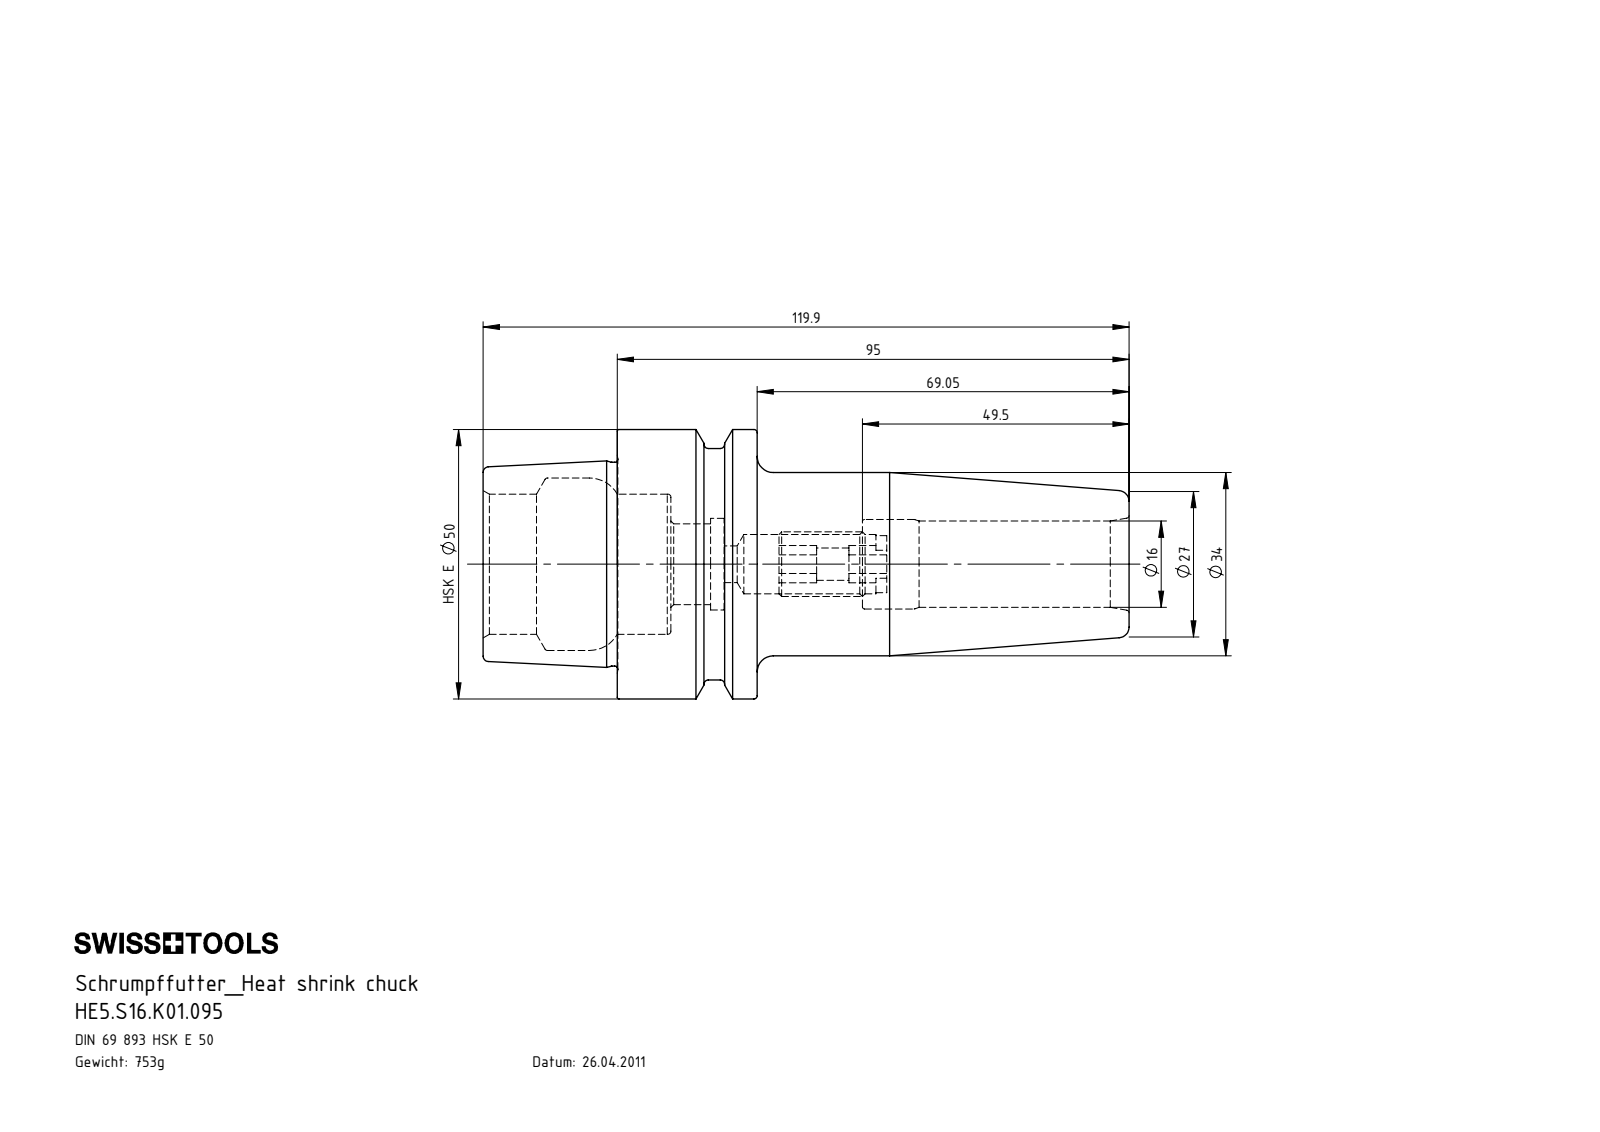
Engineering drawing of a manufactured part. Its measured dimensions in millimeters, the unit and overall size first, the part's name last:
Units: millimetres
Overall size (bounding box): 119.9 × 50 × 50
Round holes (diameter × count): ⌀6 ×1, ⌀6.8 ×1, ⌀11 ×1, ⌀15 ×1, ⌀16 ×1, ⌀16.6 ×1, ⌀17 ×1, ⌀26 ×1, ⌀32 ×1
Round bosses / shafts (diameter × count): ⌀50 ×1, ⌀42.95 ×1, ⌀37.81 ×1, ⌀34 ×1, ⌀12 ×1
Main face-to-face distances: 25.95, 24.9, 50.85, 34.85, 9.95, 16, 44.7, 19.8, 9.85, 6.15
Volume: 95 910 mm³ · Surface area: 25 914 mm²
Bodies: 2 solids, 142 faces (43 planar, 34 cylindrical, 65 other)
Part name (STEP PRODUCT): ERU-AN5.K01.020_A; HE5.S16.K01.095; HE5-S16.K01.095_B_Fertigbearbeitung
STEP written by: SolidWorks 2017 (AUTOMOTIVE_DESIGN)
